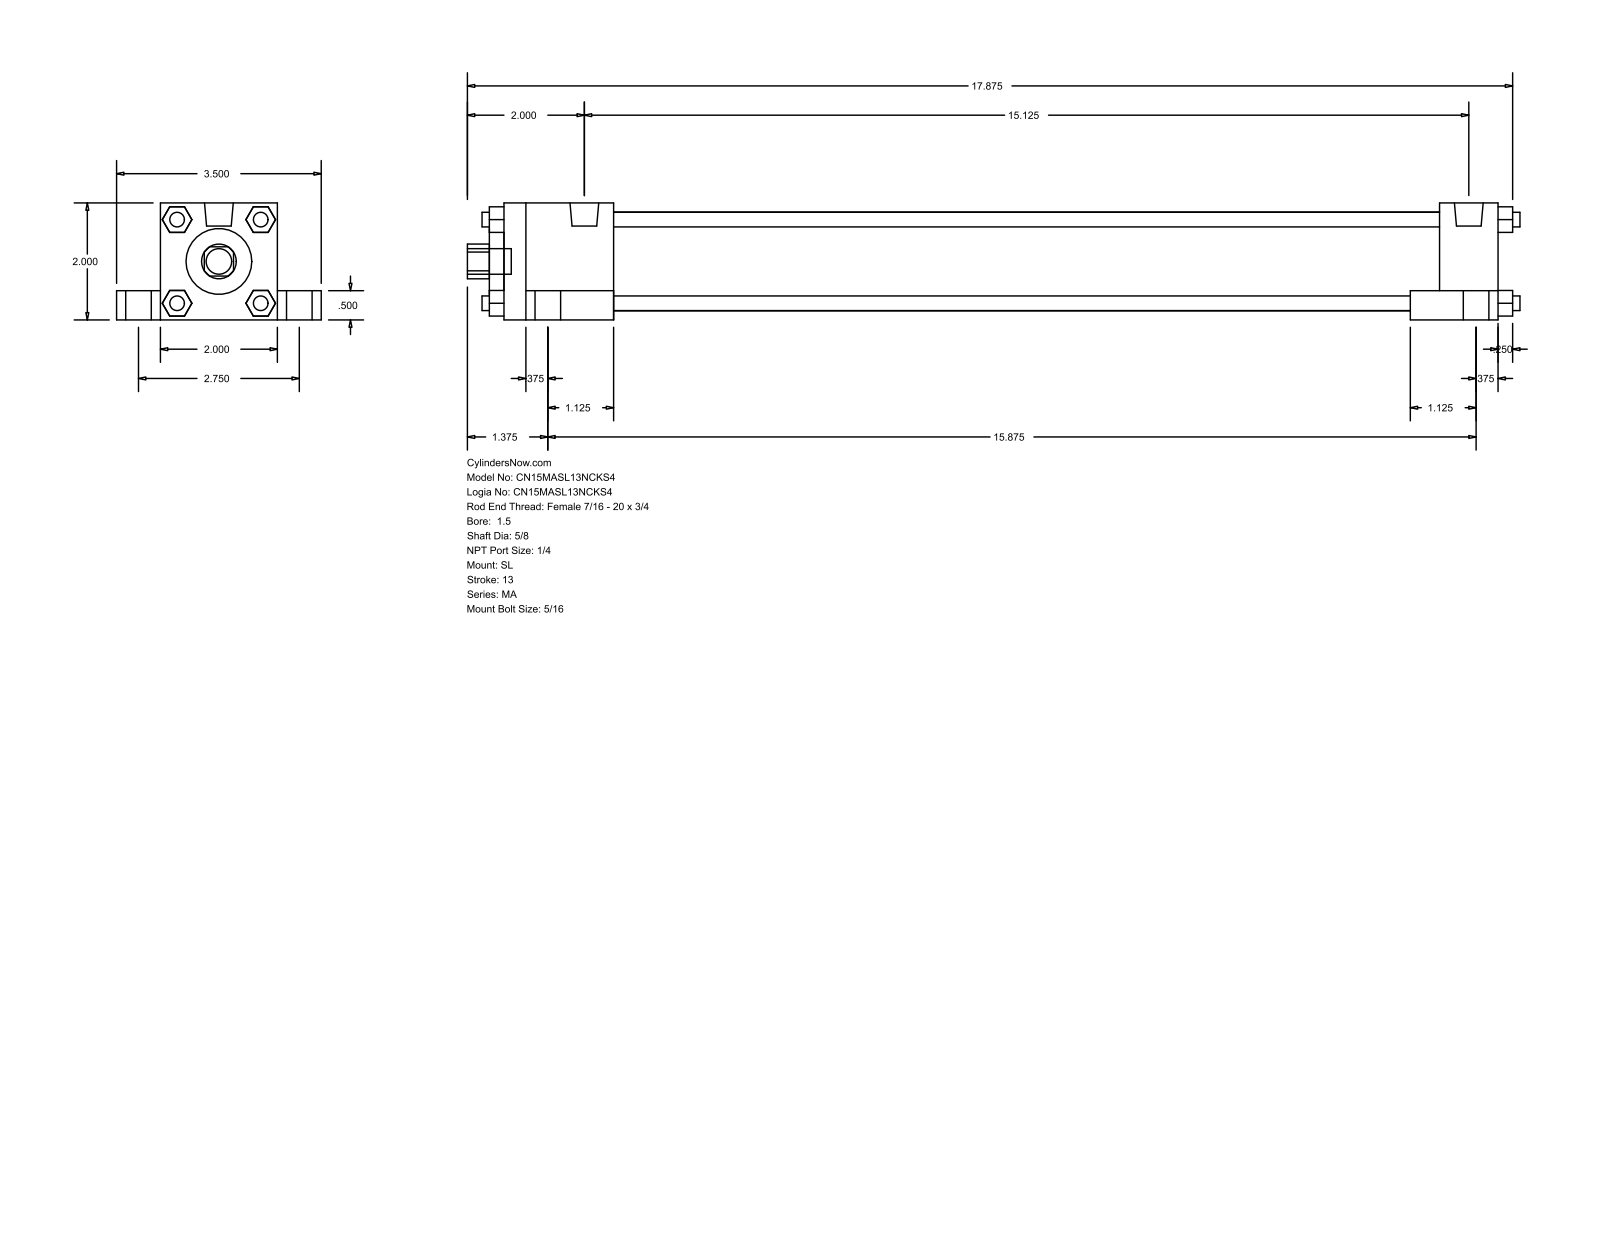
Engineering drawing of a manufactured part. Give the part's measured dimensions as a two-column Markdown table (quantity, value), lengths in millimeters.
| quantity | value |
| --- | --- |
| part name | MA_SL__0150_0.625 |
| STEP written by | GSSL Pune (CONFIG_CONTROL_DESIGN) |
| units | millimeters |
| bodies | 0 solids, 148 faces (112 planar, 36 cylindrical, 0 other) |
| overall size | 457.2 × 88.9 × 50.8 |
| round holes (diameter × count) | 15.88 × 1, 28.57 × 1, 42.93 × 1 |
| round bosses / shafts (diameter × count) | 11.11 × 5, 17.46 × 4, 7.94 × 4, 6.35 × 4, 12.49 × 2 |
| partial cylindrical surfaces (radius × count) | 7.54 × 1 |
| main face-to-face distances | 50.8, 19.05, 38.1, 12.7, 431.8, 69.85, 358.77, 9.52, 406.39, 25.41 |
